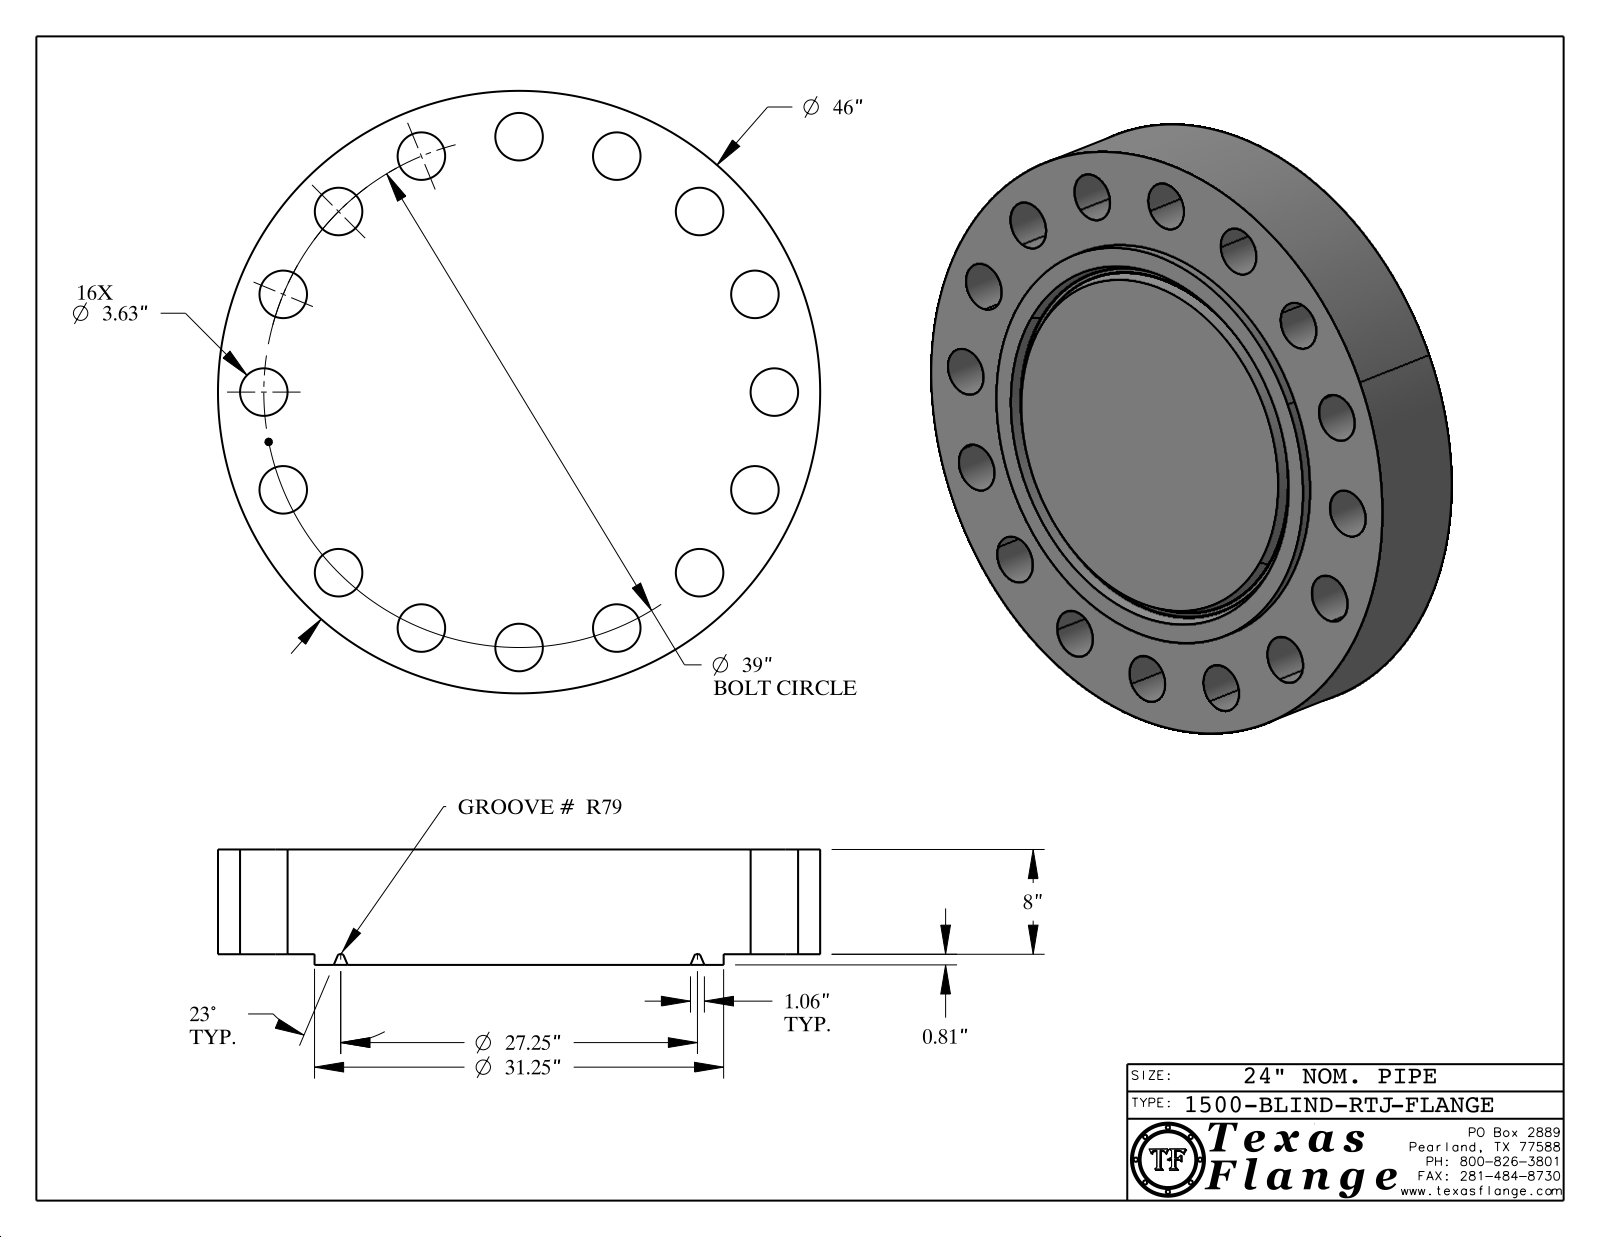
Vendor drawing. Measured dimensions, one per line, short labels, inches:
name: 1500-BLIND-RTJ
written by: CATIA V5 STEP AP214 (AUTOMOTIVE_DESIGN)
unit: in
bodies: 1 solid, 434 faces (370 planar, 56 cylindrical, 8 other)
size: 46 × 46 × 8.813
volume: 12 544 in³; area: 5 778 in²
holes: 16× ⌀3.63, 1× ⌀0.495
bosses: 8× ⌀0.03, 1× ⌀46, 1× ⌀31.25, 1× ⌀0.39
face distances: 8, 0.813, 8.813, 8.798, 7.985, 0.015, 0.148, 0.145, 0.027, 0.096
hole spacings: 21.667, 27.577, 38.251, 14.925, 36.031, 7.608, 7.609, 32.427
